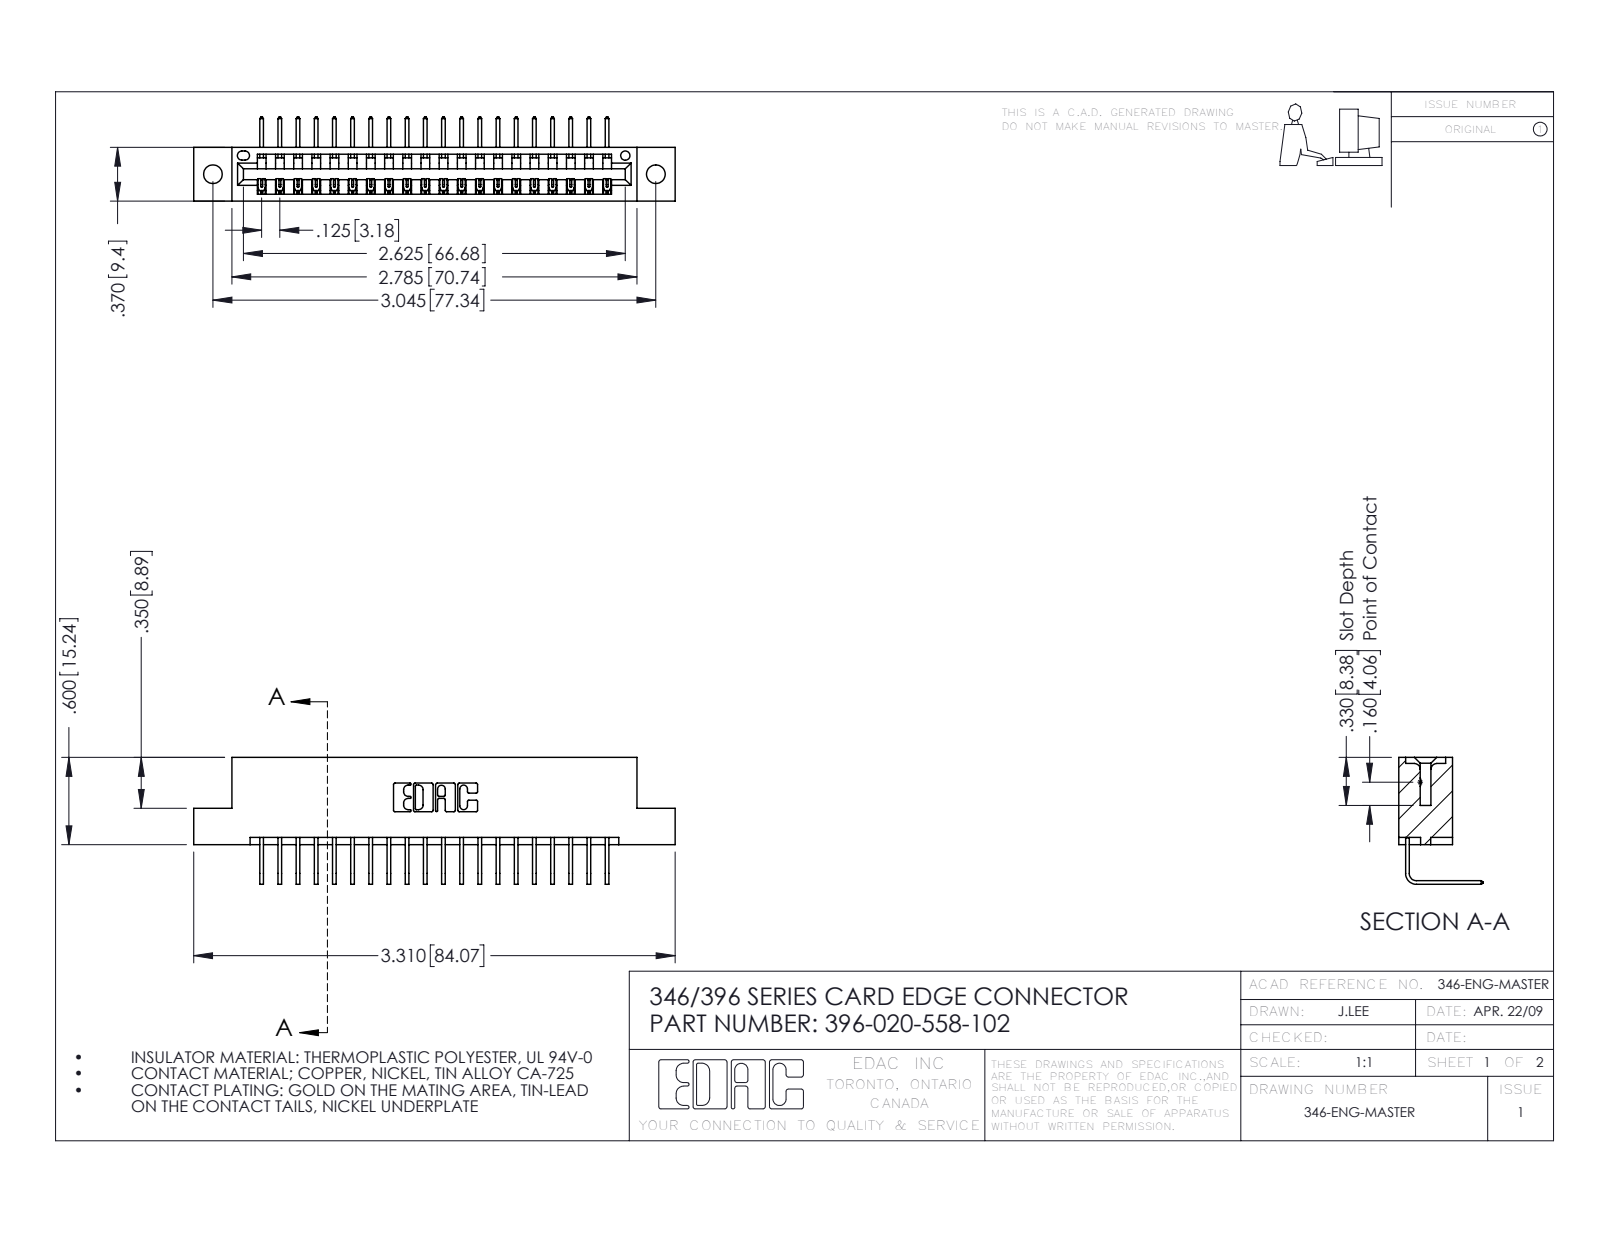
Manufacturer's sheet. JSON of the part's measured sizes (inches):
{"part_name": "396-020-558-102; 345-292-001_558 Tail - 2; 346 Part_Flush Mounting Lugs - 0.128 Dia", "step_written_by": "SolidWorks 2016 (CONFIG_CONTROL_DESIGN)", "units": "inches", "bodies": {"solids": 21, "faces": 1322, "planar": 916, "cylindrical": 406, "other": 0}, "overall_size": [3.31, 0.873, 0.58], "volume_in3": 0.484, "surface_area_in2": 15.18, "round_holes": [[0.128, 2], [0.064, 1]], "partial_cylinders_radius": [[0.006, 40], [0.01, 22], [0.007, 6], [0.031, 6], [0.026, 3], [0.031, 2], [0.04, 2], [0.014, 1]], "face_to_face_distances": [0.322, 0.048, 0.37, 0.25, 0.298, 0.025, 0.072, 0.148, 0.222, 0.1], "hole_center_spacings": [0.246, 2.837, 3.045]}
